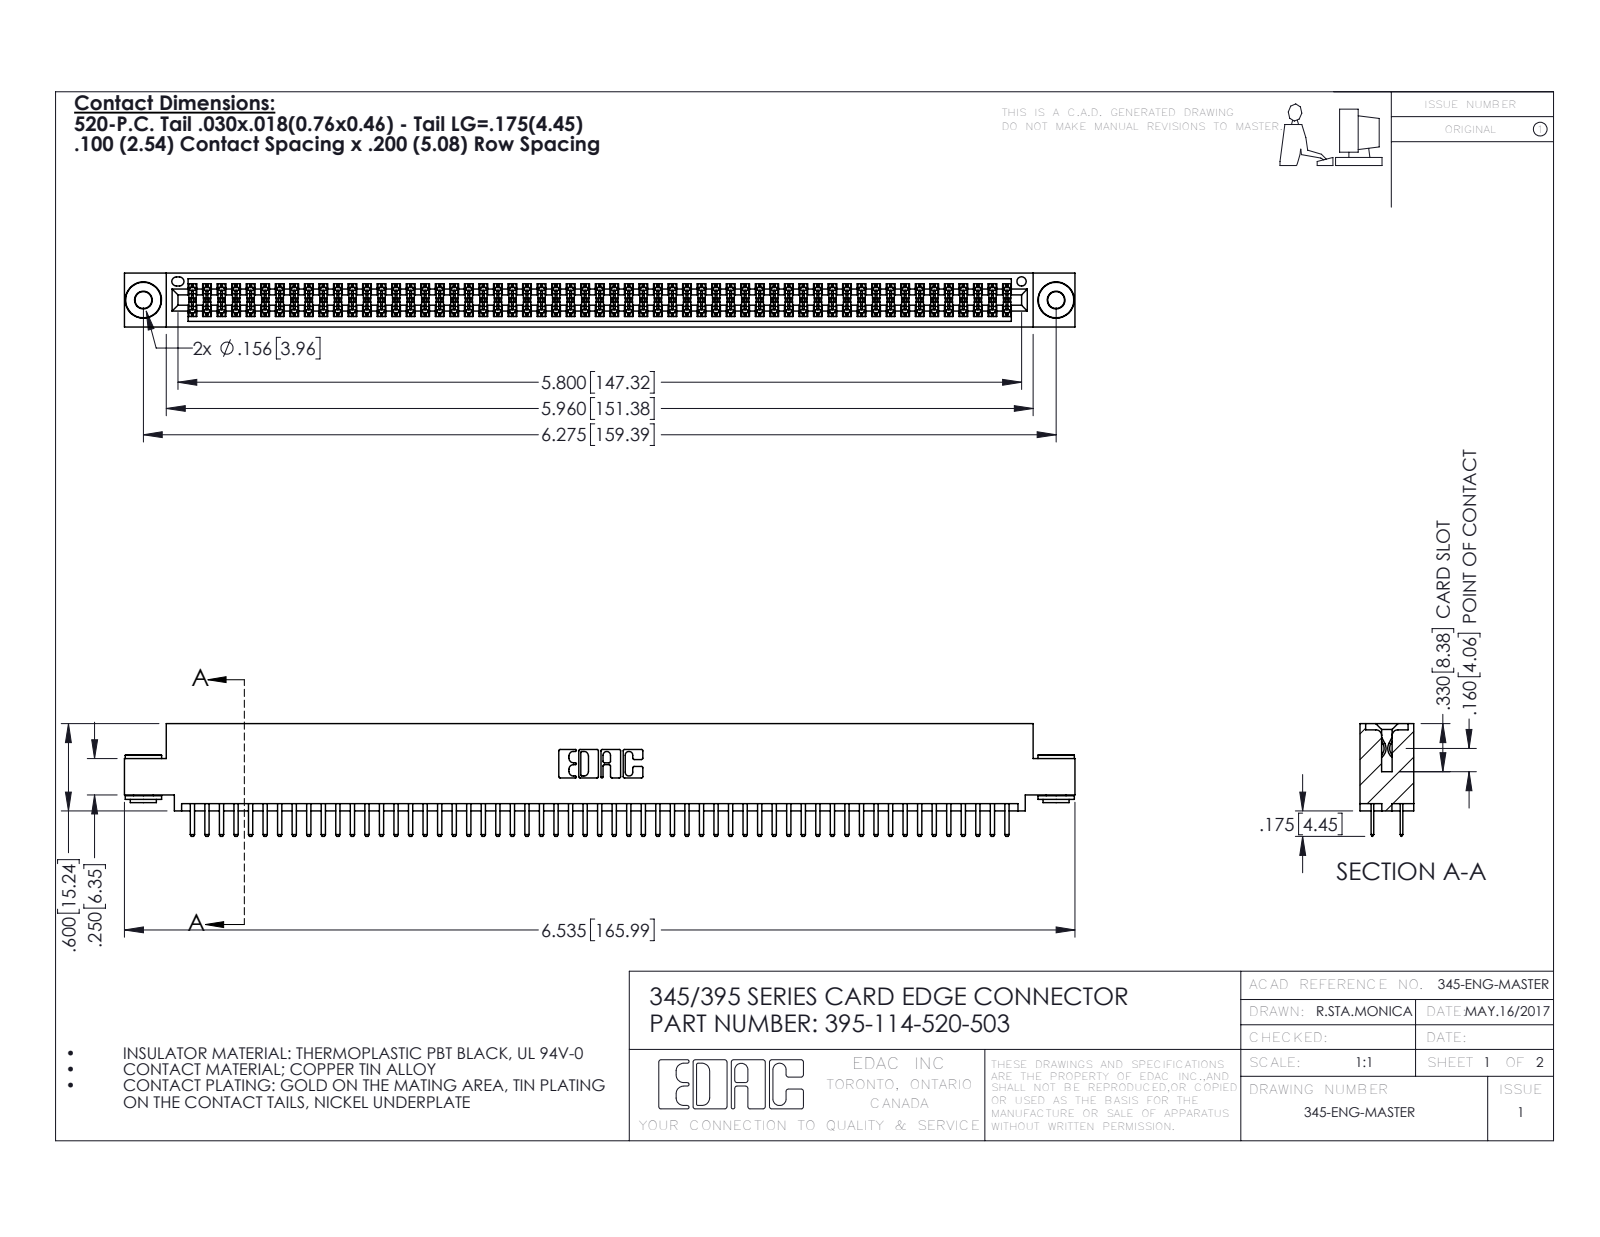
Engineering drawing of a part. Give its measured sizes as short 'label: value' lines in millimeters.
name: 345-292-001_345-293-120; 395-114-520-503; 345-250-002_345-250-002-102; 345 Part_0.110 Offset - 0.156 Dia-TH
written by: SolidWorks 2016 (CONFIG_CONTROL_DESIGN)
unit: mm
bodies: 117 solids, 6324 faces (4084 planar, 2232 cylindrical, 8 other)
size: 166 × 19.7 × 9.4
volume: 16 200 mm³; area: 24 370 mm²
holes: 2× ⌀2.9, 2× ⌀4, 1× ⌀1.6
bosses: 2× ⌀6.4, 2× ⌀4.6, 2× ⌀3.5
rounds: 171× R0.2, 118× R0.3, 22× R0.3, 6× R0.2, 6× R0.8, 3× R0.7, 2× R0.4, 2× R0.5
face distances: 1.8, 7.6, 5.1, 9.4, 0.6, 2.5, 6.9, 5.7, 0.6, 1.8
hole spacings: 6.9, 153.4, 159.4
